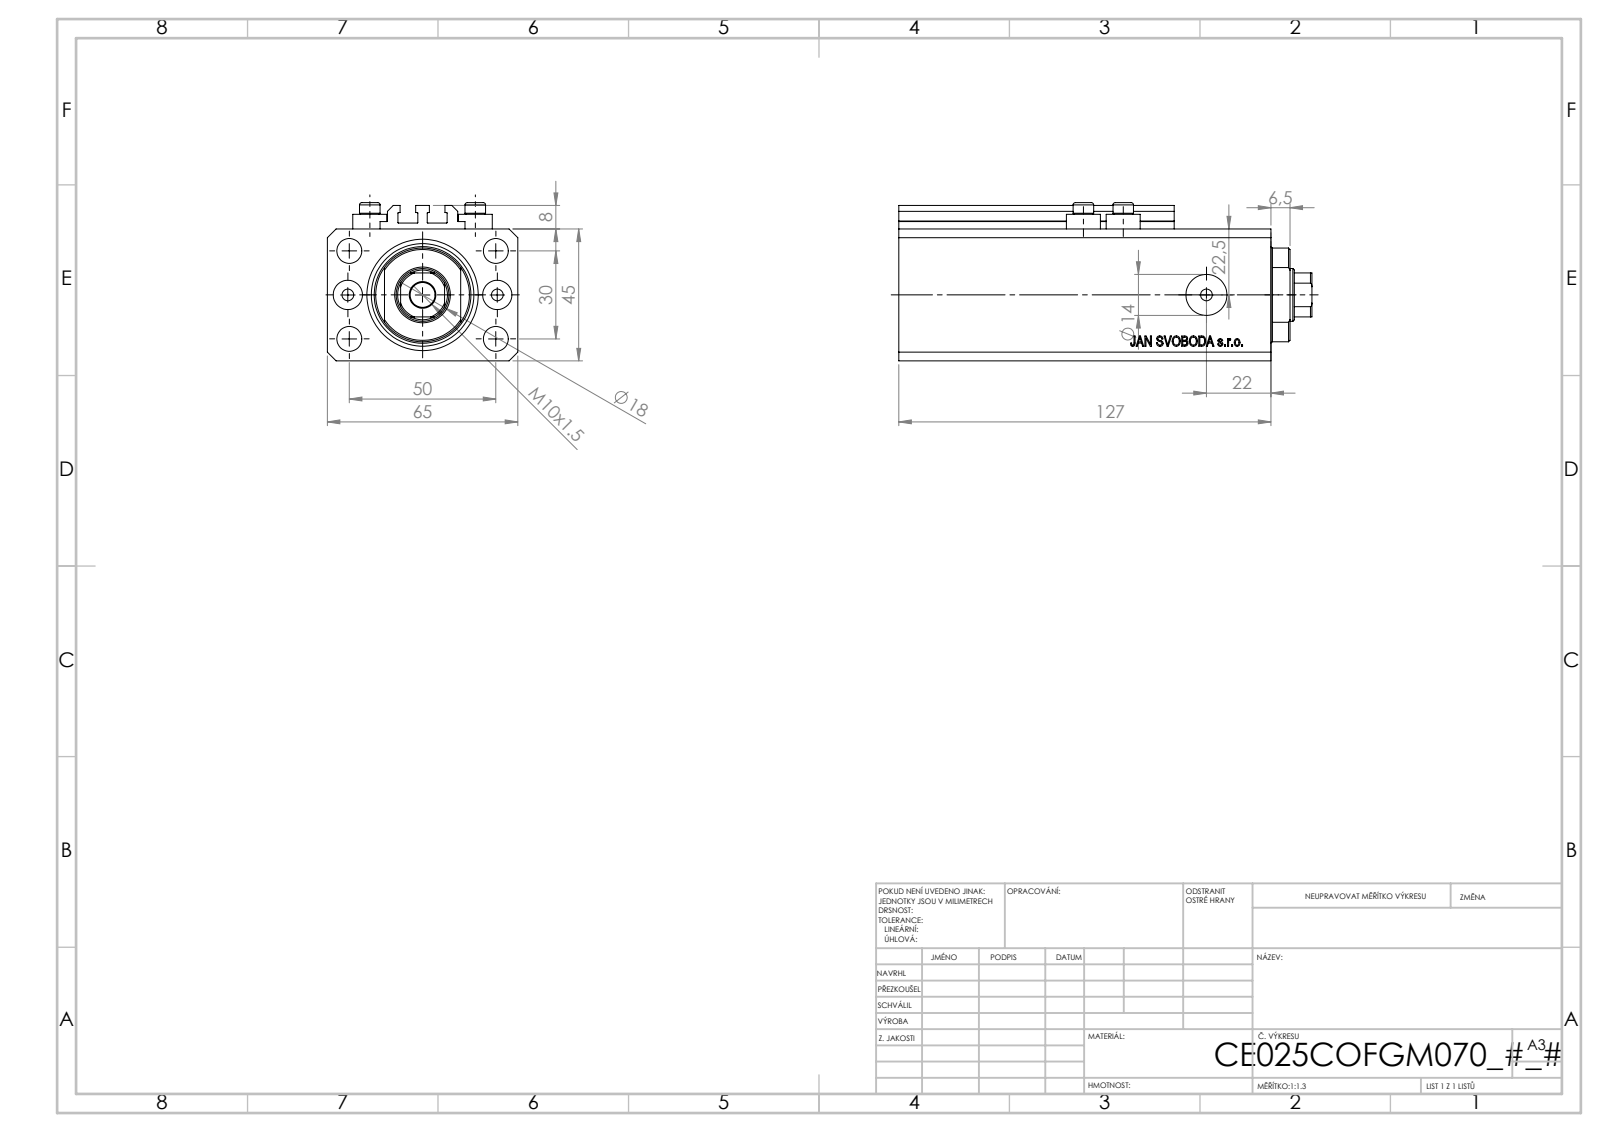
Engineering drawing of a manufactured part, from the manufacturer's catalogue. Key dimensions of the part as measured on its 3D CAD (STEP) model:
Part name (STEP PRODUCT): V250CE_C_VCP; V250CE_VC_C; ALLEN BOLT V250CE; V250CE_C_Body
STEP written by: SolidWorks 2019 (CONFIG_CONTROL_DESIGN)
Units: millimetres
Bodies: 8 solids, 1034 faces (504 planar, 86 cylindrical, 444 other)
Overall size (bounding box): 141 × 65 × 54
Volume: 340 429 mm³ · Surface area: 85 049 mm²
Round holes (diameter × count): ⌀4 ×8, ⌀8.5 ×5, ⌀10 ×2, ⌀14 ×2, ⌀18 ×1, ⌀25 ×1, ⌀38 ×1
Round bosses / shafts (diameter × count): ⌀11.6 ×4, ⌀7 ×4
Partial cylindrical surfaces — rounded edges, fillets, slot ends (radius × count): R0.2 ×10, R8.5 ×1, R16 ×1
Main face-to-face distances: 45, 65, 14, 47, 113, 127, 2.5, 2, 10, 20.5
Hole centre spacings: 15.01, 29.15, 52.68, 13.6, 25.5, 30, 36, 38.48
